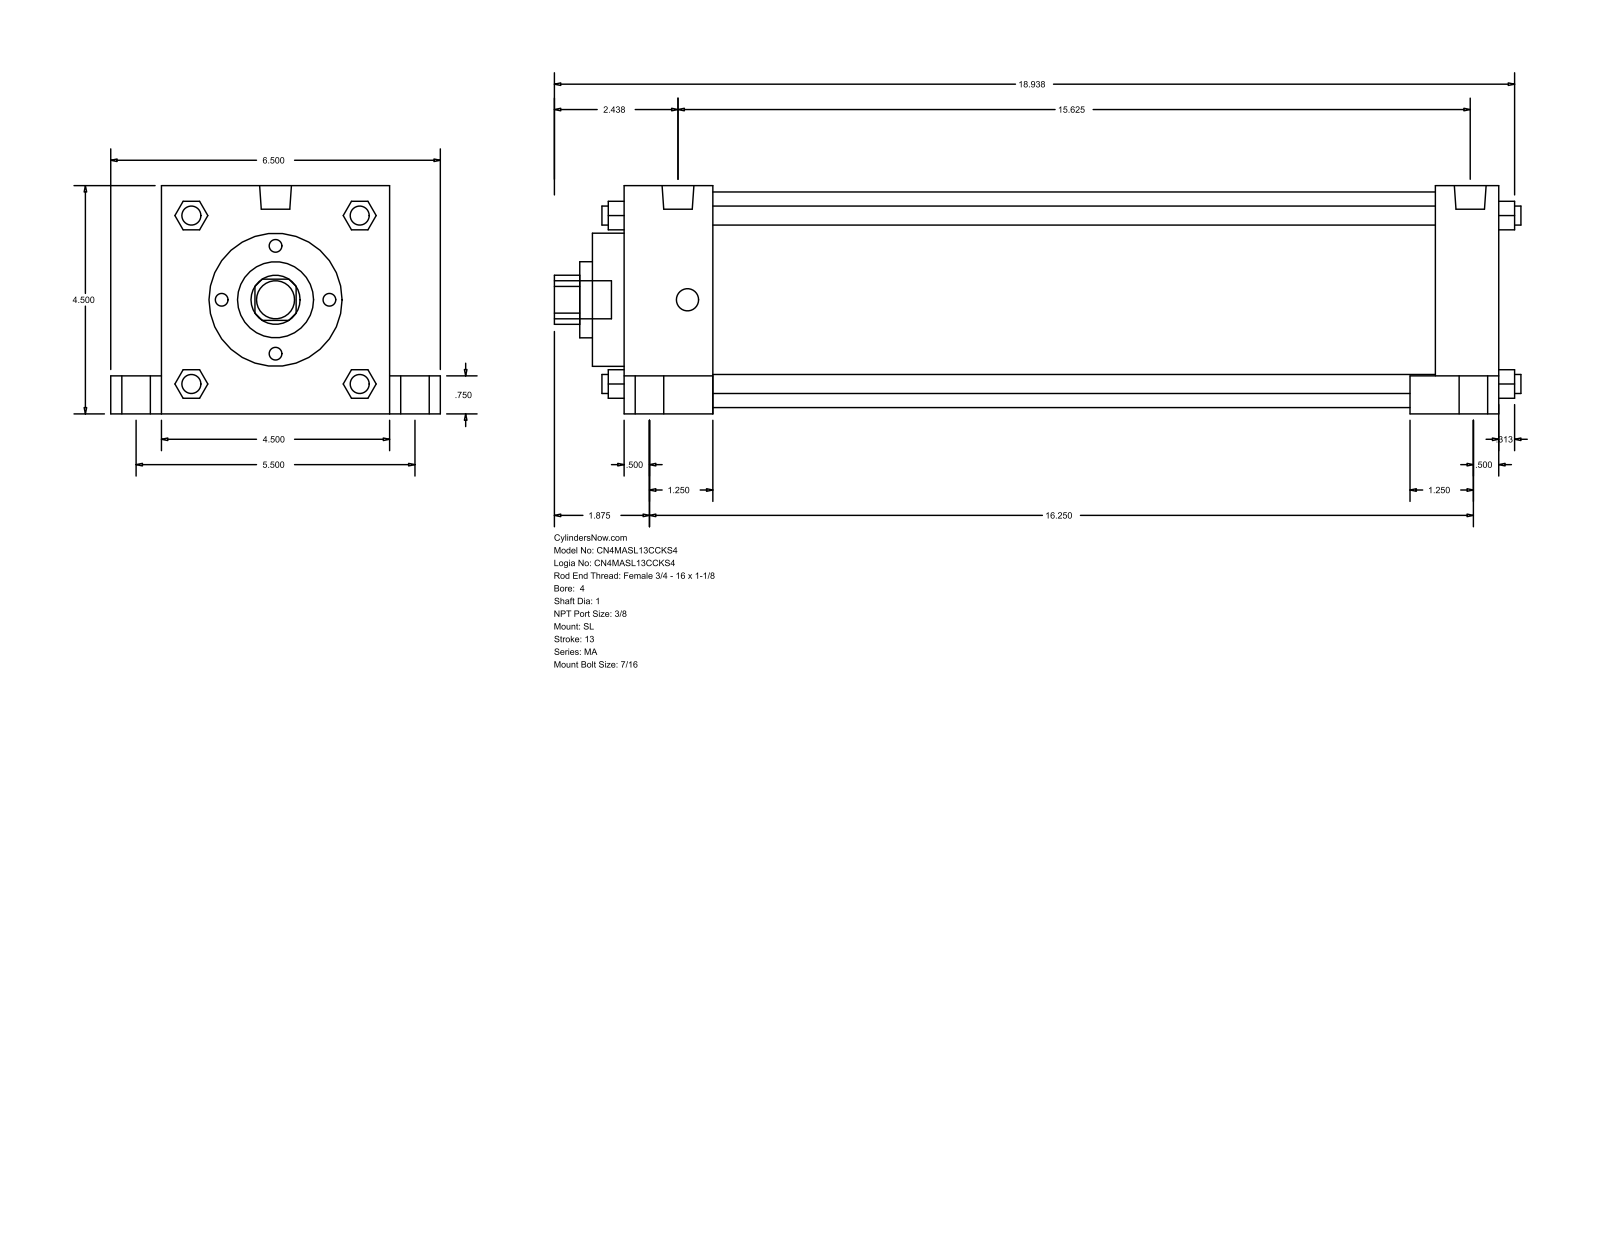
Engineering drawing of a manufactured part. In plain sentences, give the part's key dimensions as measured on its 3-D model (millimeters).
The part is named "MA_SL__0400_1". Its 3-D file was written by "GSSL Pune (CONFIG_CONTROL_DESIGN)". It is 0 solids with 150 faces: 113 planar, 37 cylindrical and 0 other. Overall it measures 484.19 by 165.1 by 114.3 millimeters. Round holes: 1 of diameter 25.4, 1 of diameter 38.1, 1 of diameter 66.67, 1 of diameter 107.95. Round bosses or shafts: 4 of diameter 20.64, 4 of diameter 14.29, 4 of diameter 11.11, 4 of diameter 9.53, 2 of diameter 15.93, 1 of diameter 19.05. Partial cylindrical surfaces (rounded edges, fillets, slot ends): 1 of radius 12.29. The main face-to-face distances are 114.3, 438.15, 44.46, 393.69, 406.4, 361.94, 31.75, 25.4, 139.7, 454.02.
